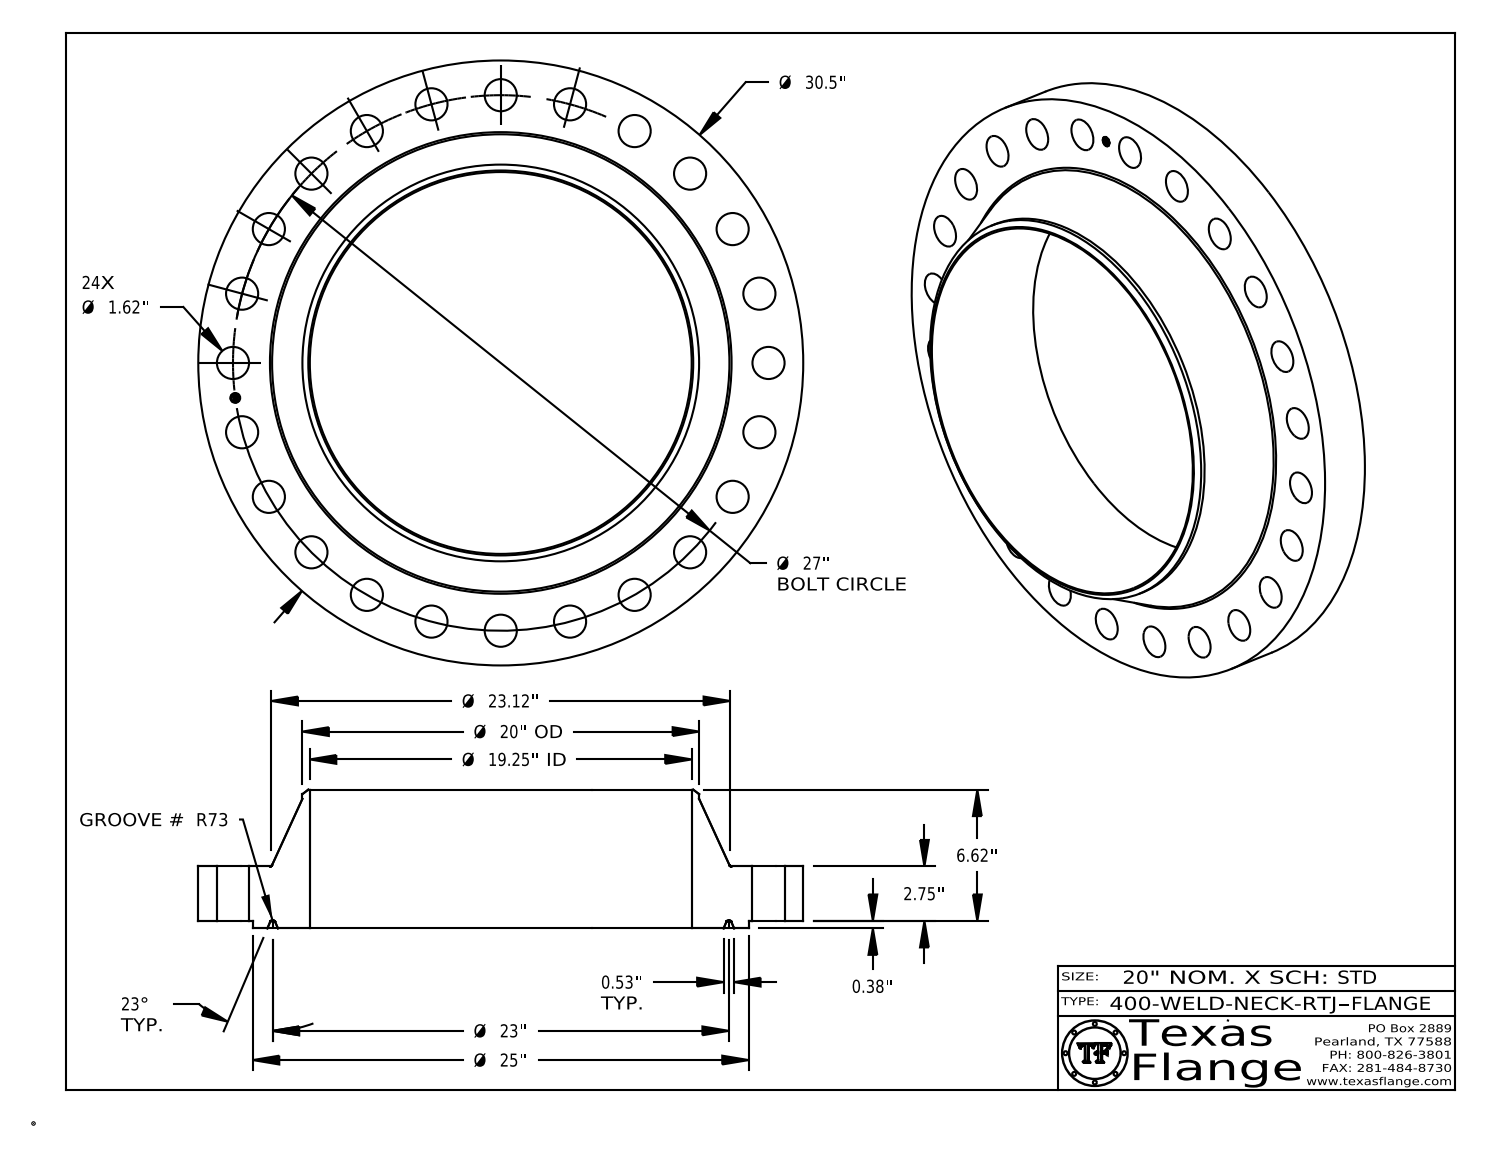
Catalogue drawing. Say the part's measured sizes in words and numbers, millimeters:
The part is named "400-WELD-NECK-RTJ". Its 3-D file was written by "CATIA V5 STEP AP214 (AUTOMOTIVE_DESIGN)". It is 1 solid with 461 faces: 371 planar, 76 cylindrical and 14 other. Overall it measures 774.7 by 774.7 by 177.7 millimeters. Its volume is 22 960 000 cubic millimeters and its surface area 1 312 000 square millimeters. Round holes: 24 of diameter 41.1, 1 of diameter 12.6, 1 of diameter 489. Round bosses or shafts: 8 of diameter 0.8, 1 of diameter 774.7, 1 of diameter 635, 1 of diameter 508, 1 of diameter 9.9. The main face-to-face distances are 69.9, 9.5, 79.4, 177.7, 168.1, 98.3, 79, 69.5, 0.4, 98.7. The hole center spacings are 342.9, 89.5, 177.5, 262.5, 417.5, 633.6, 679.9, 544.1.
